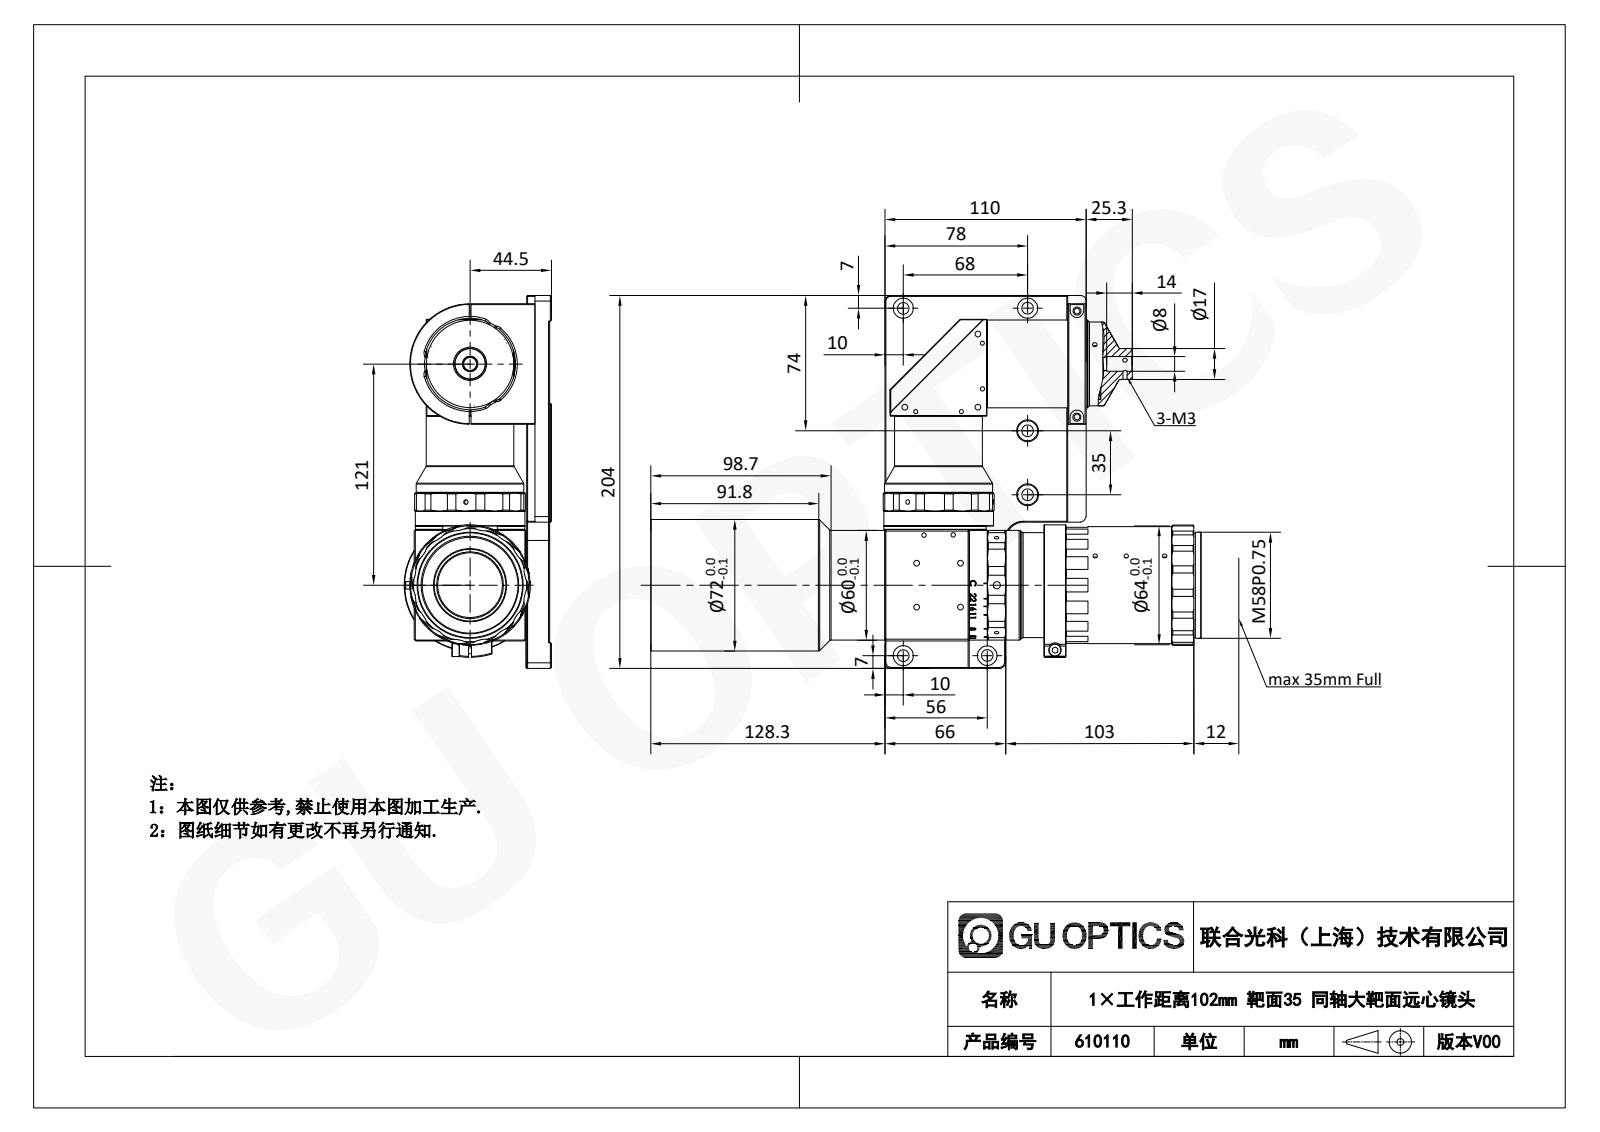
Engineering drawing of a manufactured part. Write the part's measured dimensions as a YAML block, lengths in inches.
part_name: "DTCA35F-44C-G-M58-AL(8)"
step_written_by: "SolidWorks 2017 (CONFIG_CONTROL_DESIGN)"
units: inches
bodies: {solids: 1, faces: 1311, planar: 386, cylindrical: 458, other: 467}
overall_size: [11.862, 8.031, 3.169]
volume: 97.03
surface_area: 273.5
round_holes:
  - {diameter: 0.098, count: 22}
  - {diameter: 0.13, count: 15}
  - {diameter: 0.094, count: 13}
  - {diameter: 0.177, count: 12}
  - {diameter: 0.295, count: 9}
  - {diameter: 0.256, count: 6}
  - {diameter: 0.433, count: 6}
  - {diameter: 0.126, count: 4}
  - {diameter: 0.236, count: 4}
  - {diameter: 0.087, count: 2}
  - {diameter: 0.059, count: 1}
  - {diameter: 0.134, count: 1}
round_bosses_or_shafts:
  - {diameter: 2.362, count: 2}
  - {diameter: 1.89, count: 2}
  - {diameter: 0.157, count: 2}
  - {diameter: 2.835, count: 1}
  - {diameter: 2.598, count: 1}
  - {diameter: 2.52, count: 1}
  - {diameter: 2.441, count: 1}
  - {diameter: 2.402, count: 1}
partial_cylinders:
  - {radius: 0.591, count: 32}
  - {radius: 0.118, count: 11}
  - {radius: 0.079, count: 10}
  - {radius: 0.039, count: 2}
  - {radius: 0.148, count: 2}
  - {radius: 0.061, count: 1}
  - {radius: 0.157, count: 1}
  - {radius: 0.394, count: 1}
face_to_face_distances: [0.492, 0.039, 0.531, 2.913, 2.146, 4.331, 2.421, 0.256, 2.953, 0.807]
hole_center_spacings: [1.63, 0.945, 0.028, 1.575, 1.63, 1.642, 2.267, 0.196]
